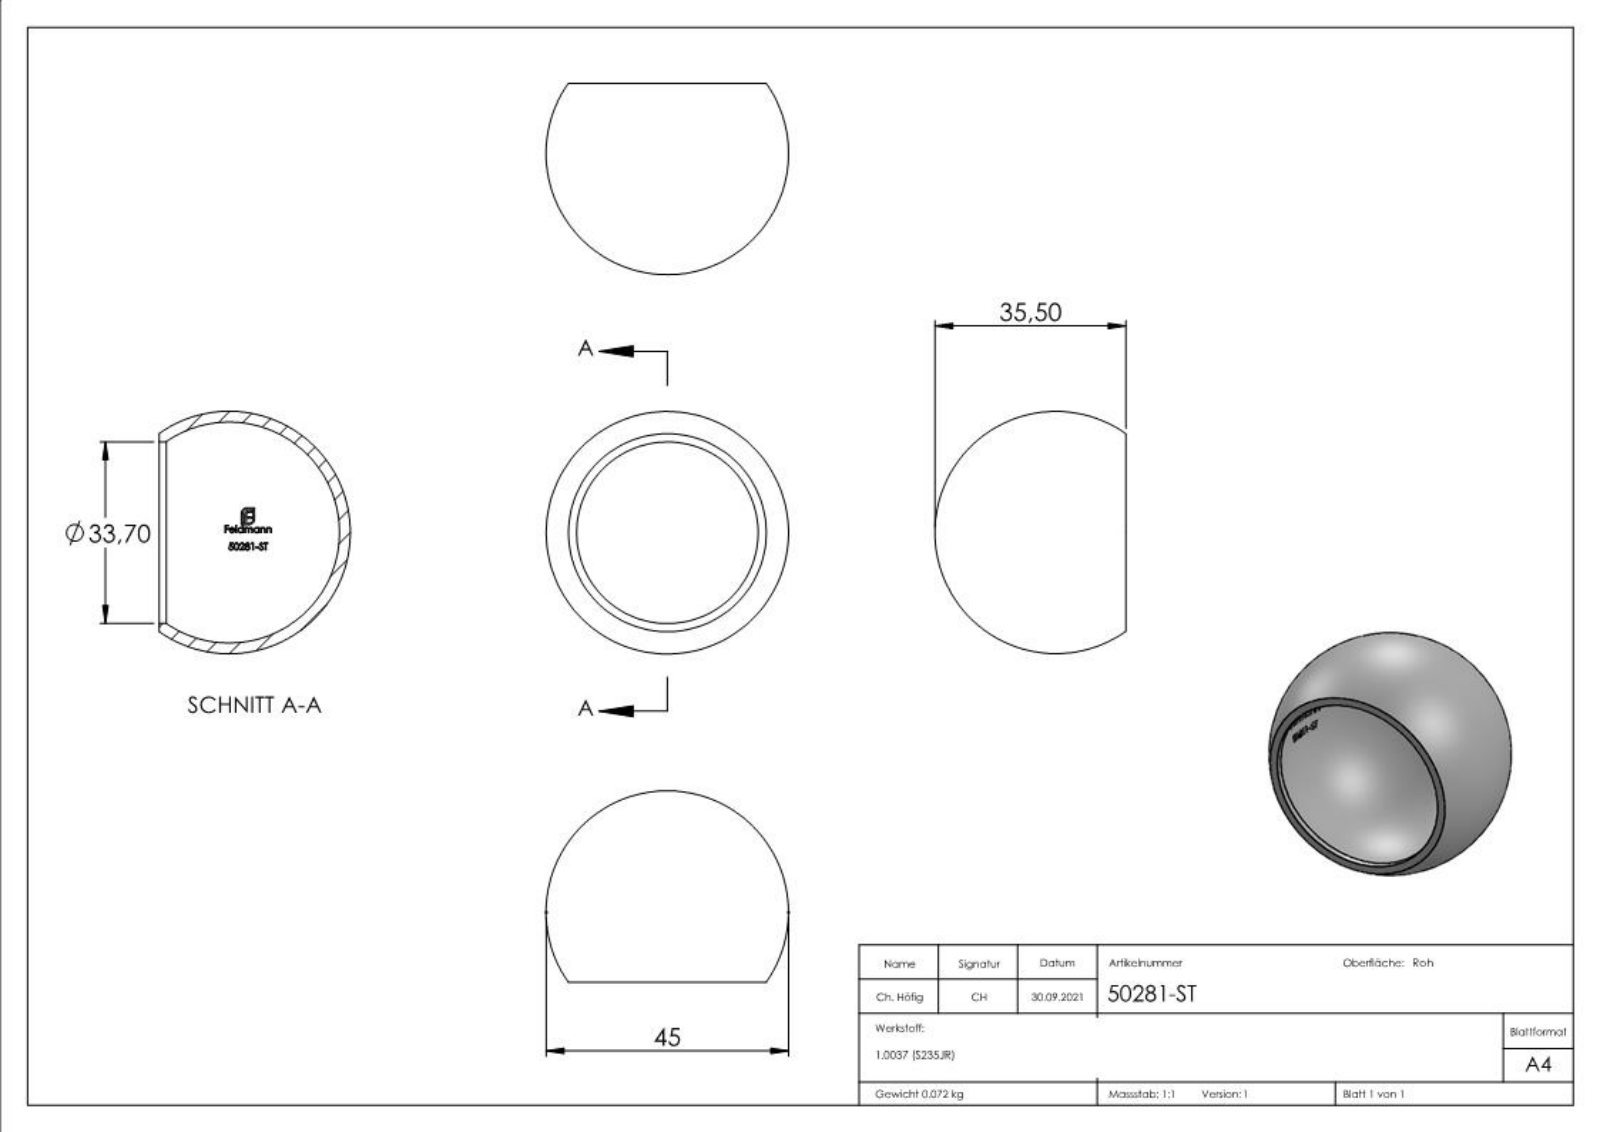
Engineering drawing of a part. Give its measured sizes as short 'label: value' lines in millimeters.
name: 50281-ST
written by: SolidWorks 2018 (CONFIG_CONTROL_DESIGN)
unit: mm
bodies: 1 solid, 258 faces (109 planar, 1 cylindrical, 148 other)
size: 45 × 45 × 35.5
volume: 9 258 mm³; area: 9 483 mm²
holes: 1× ⌀33.7
face distances: 1.86, 1.64, 3.21, 3.27, 0.34, 15.49, 2.02, 4.25, 2.39, 1.32
